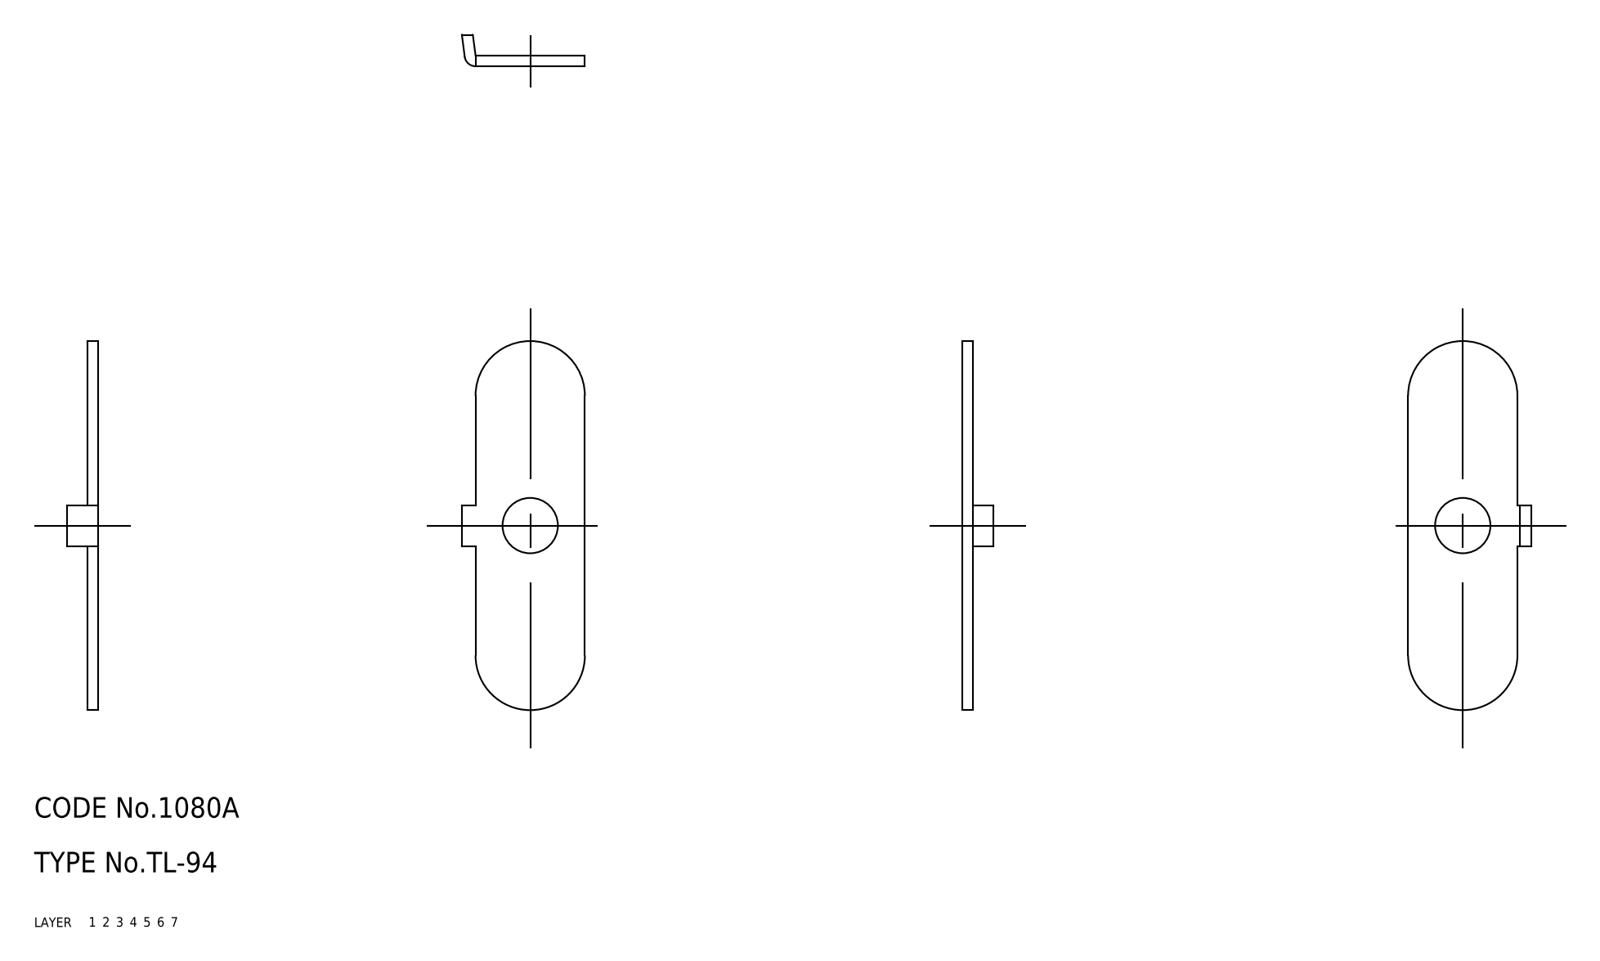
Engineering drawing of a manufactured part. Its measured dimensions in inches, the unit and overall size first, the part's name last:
Units: inches
Overall size (bounding box): 2.126 × 0.709 × 0.181
Volume: 0.076 in³ · Surface area: 2.826 in²
Bodies: 1 solid, 15 faces (0 planar, 0 cylindrical, 15 other)
Part name (STEP PRODUCT): base
STEP written by: CADfix (AUTOMOTIVE_DESIGN)
